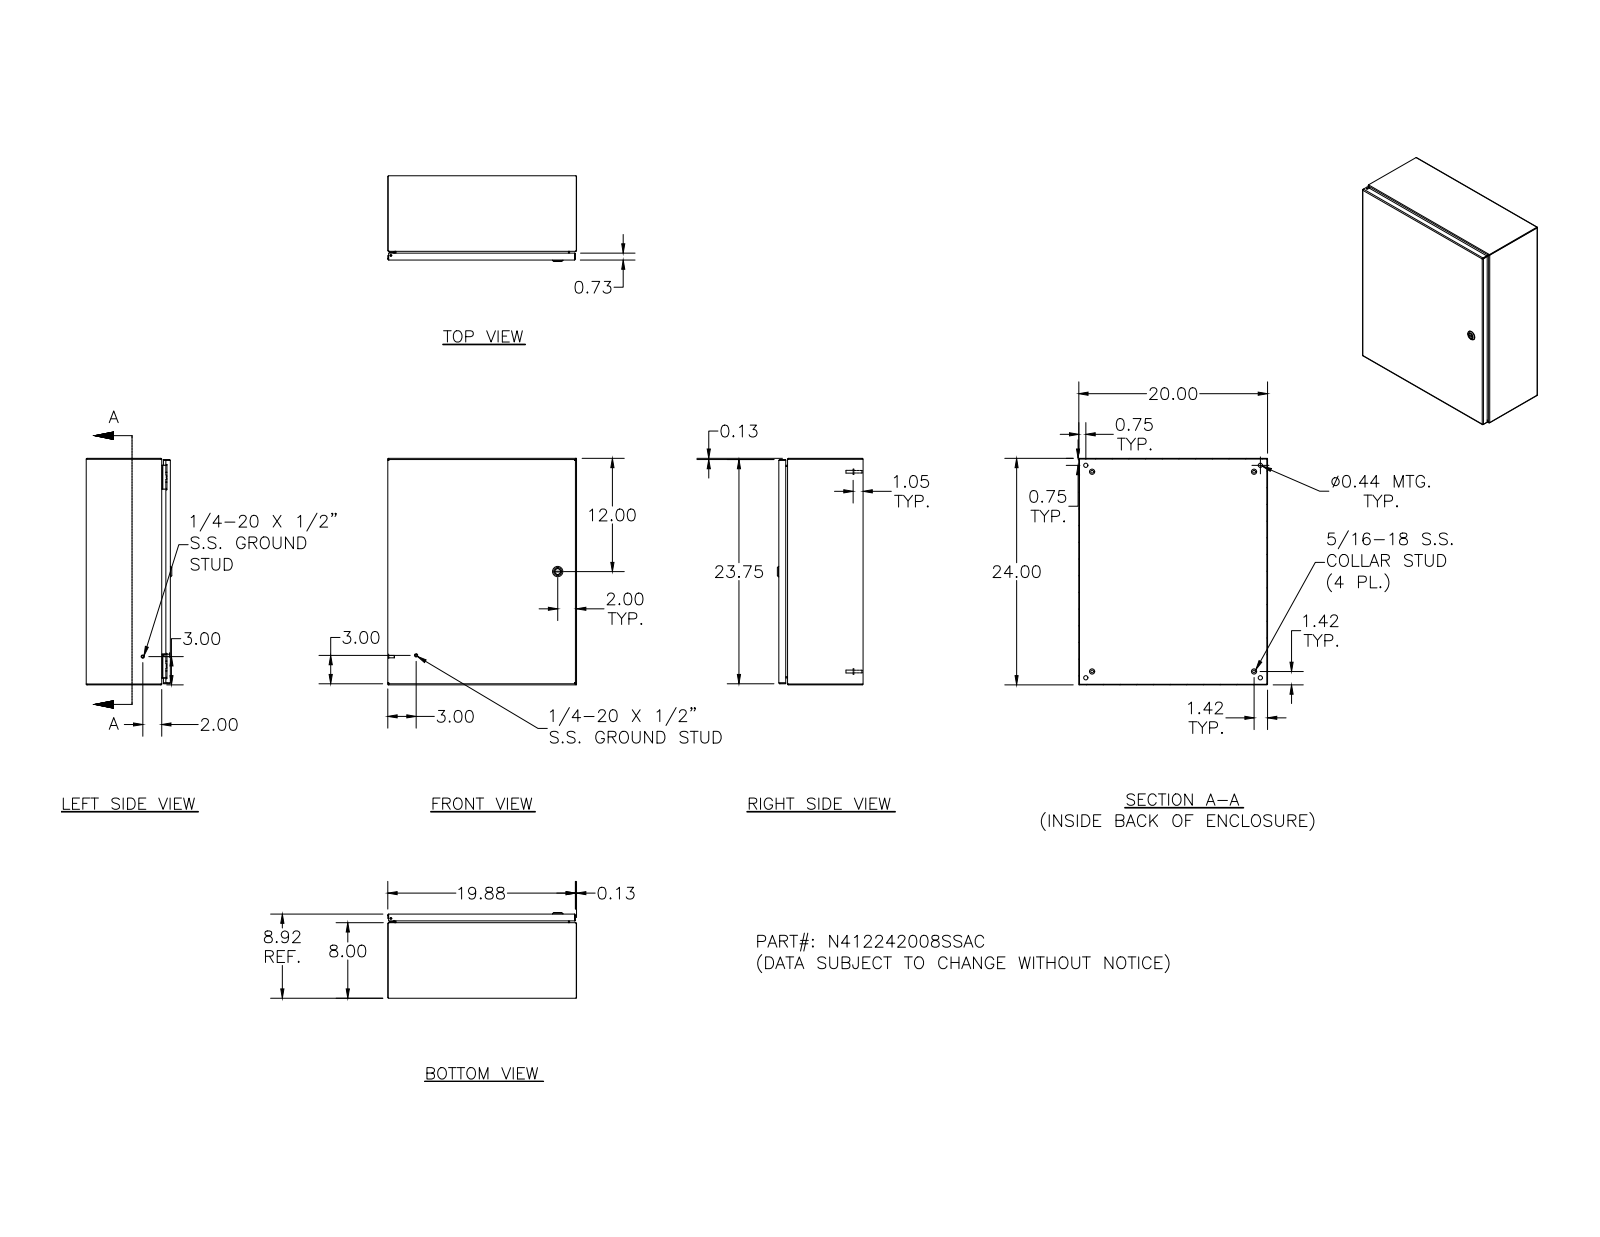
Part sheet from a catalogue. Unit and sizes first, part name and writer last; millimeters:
Units: millimetres
Overall size (bounding box): 609.6 × 508 × 230.5
Round holes (diameter × count): ⌀4.8 ×5, ⌀2.4 ×4, ⌀3.9 ×4, ⌀4.2 ×4, ⌀4.4 ×4, ⌀11.1 ×4, ⌀4 ×2, ⌀4.7 ×1, ⌀5 ×1, ⌀8 ×1, ⌀10 ×1, ⌀10.2 ×1
Round bosses / shafts (diameter × count): ⌀6.4 ×10, ⌀14.3 ×4, ⌀9.1 ×4, ⌀8.1 ×4, ⌀7.6 ×4, ⌀7 ×4, ⌀6.5 ×4, ⌀4.2 ×4
Partial cylindrical surfaces — rounded edges, fillets, slot ends (radius × count): R1.3 ×26, R0.4 ×18, R0.4 ×16, R2.3 ×16, R0.8 ×14, R3.2 ×14, R0.5 ×9, R0.8 ×8
Main face-to-face distances: 1.9, 224.6, 222.7, 226.5, 506.1, 607.7, 508, 504.2, 609.6, 605.8
Hole centre spacings: 508, 0.4, 16.8, 479.3, 0.5, 12.7, 16.5, 16.6
Volume: 2 234 000 mm³ · Surface area: 2 390 000 mm²
Bodies: 34 solids, 1364 faces (523 planar, 497 cylindrical, 344 other)
Part name (STEP PRODUCT): N412242008SSAC; N412242008SSACBKP; 388151; N4122420SSACLID (+8 more)
STEP written by: Autodesk Inventor 2011 (AUTOMOTIVE_DESIGN)
